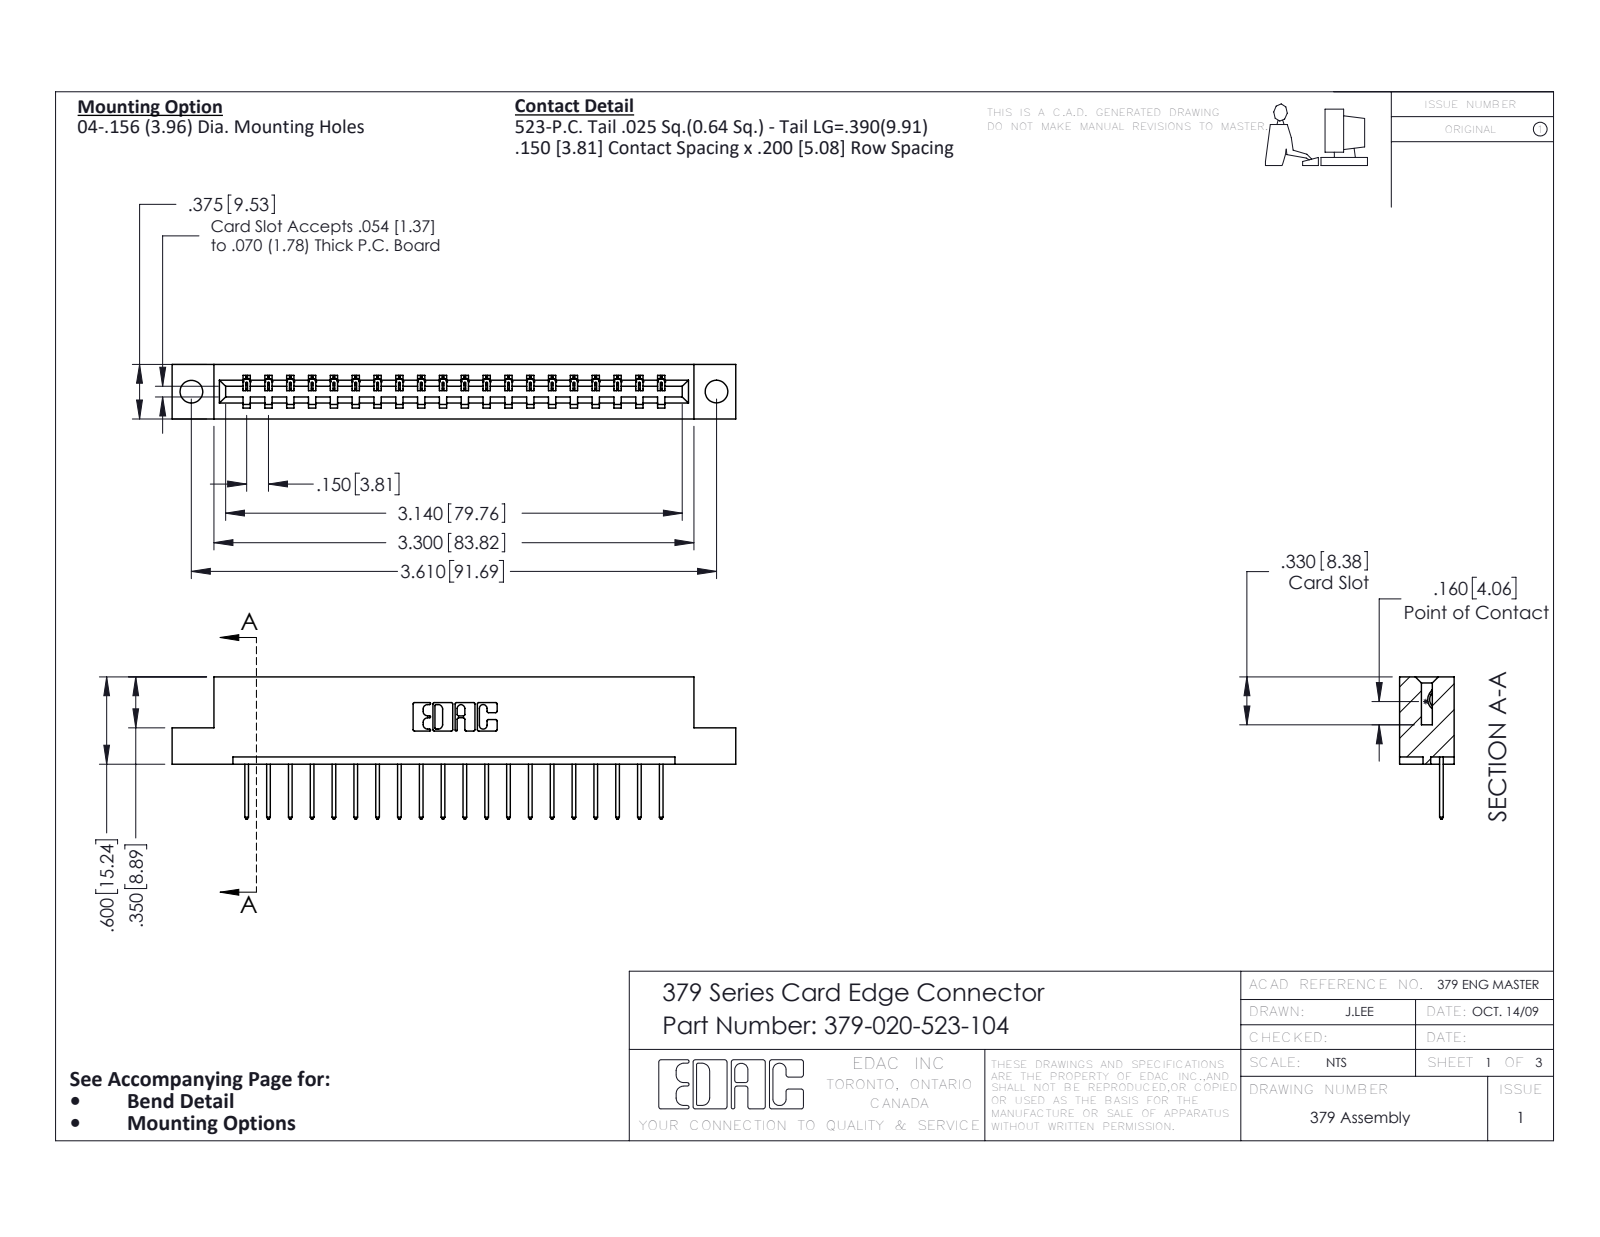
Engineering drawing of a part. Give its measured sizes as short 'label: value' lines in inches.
name: 379-020-523-104; 345-292-001_345-293-123; 379 Part_Flush - .156 Dia - TH
written by: SolidWorks 2016 (CONFIG_CONTROL_DESIGN)
unit: in
bodies: 21 solids, 1274 faces (910 planar, 364 cylindrical, 0 other)
size: 3.875 × 0.977 × 0.375
volume: 0.609 in³; area: 15.37 in²
holes: 2× ⌀0.156
rounds: 40× R0.006, 40× R0.01, 22× R0.01, 6× R0.007, 6× R0.031, 3× R0.026, 1× R0.014, 1× R0.022
face distances: 0.3, 0.075, 0.375, 0.6, 0.225, 0.15, 0.2, 0.45, 0.275, 0.1
hole spacings: 3.61
